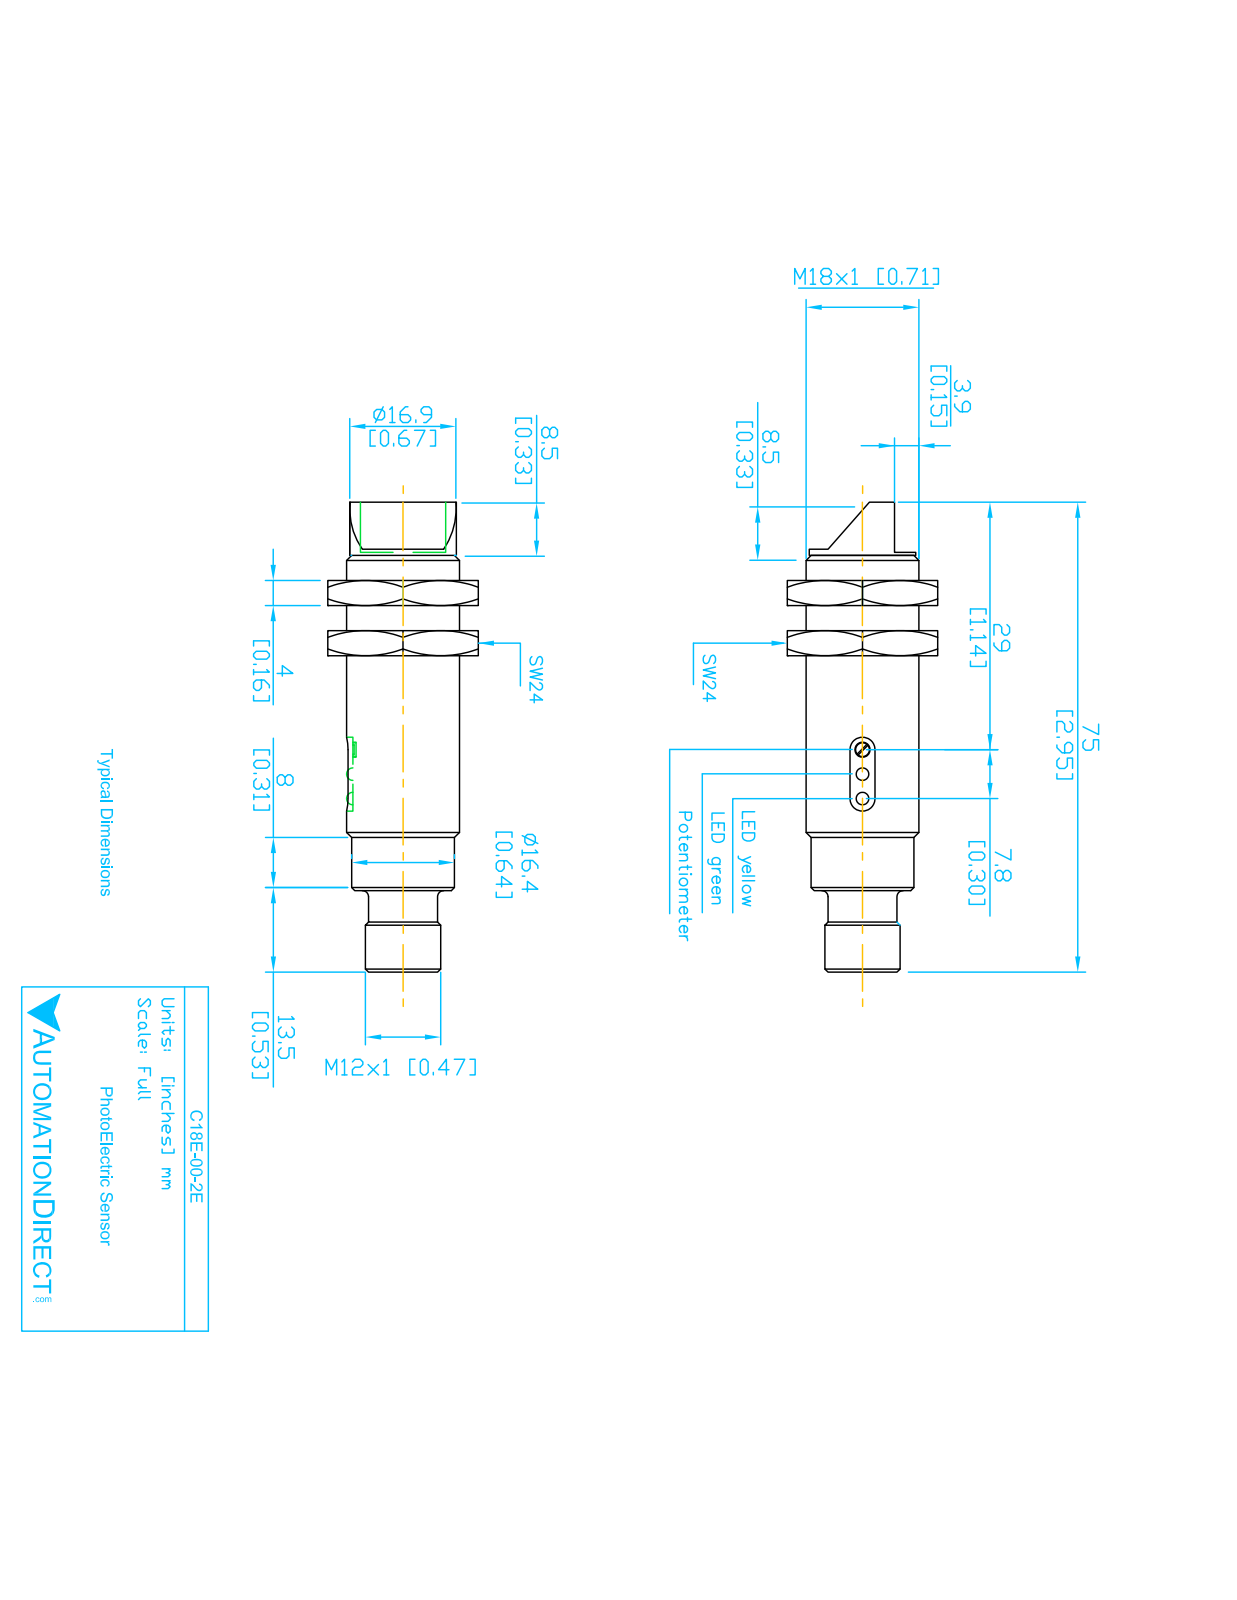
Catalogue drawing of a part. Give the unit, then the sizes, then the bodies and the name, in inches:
Units: inches
Overall size (bounding box): 2.957 × 0.709 × 0.709
Round holes (diameter × count): ⌀0.118 ×2, ⌀0.335 ×1
Round bosses / shafts (diameter × count): ⌀0.04 ×4, ⌀0.709 ×1, ⌀0.665 ×1, ⌀0.646 ×1, ⌀0.459 ×1, ⌀0.415 ×1
Partial cylindrical surfaces — rounded edges, fillets, slot ends (radius × count): R0.015 ×6, R0.02 ×2
Main face-to-face distances: 0.169, 0.512, 0.343, 2.445, 2.614, 2.957, 0.28, 2.165, 2.335, 2.677
Volume: 0.909 in³ · Surface area: 7.815 in²
Bodies: 2 solids, 68 faces (14 planar, 27 cylindrical, 27 other)
Part name (STEP PRODUCT): C18E-00-2E
STEP written by: SolidWorks 2017 (AUTOMOTIVE_DESIGN)
